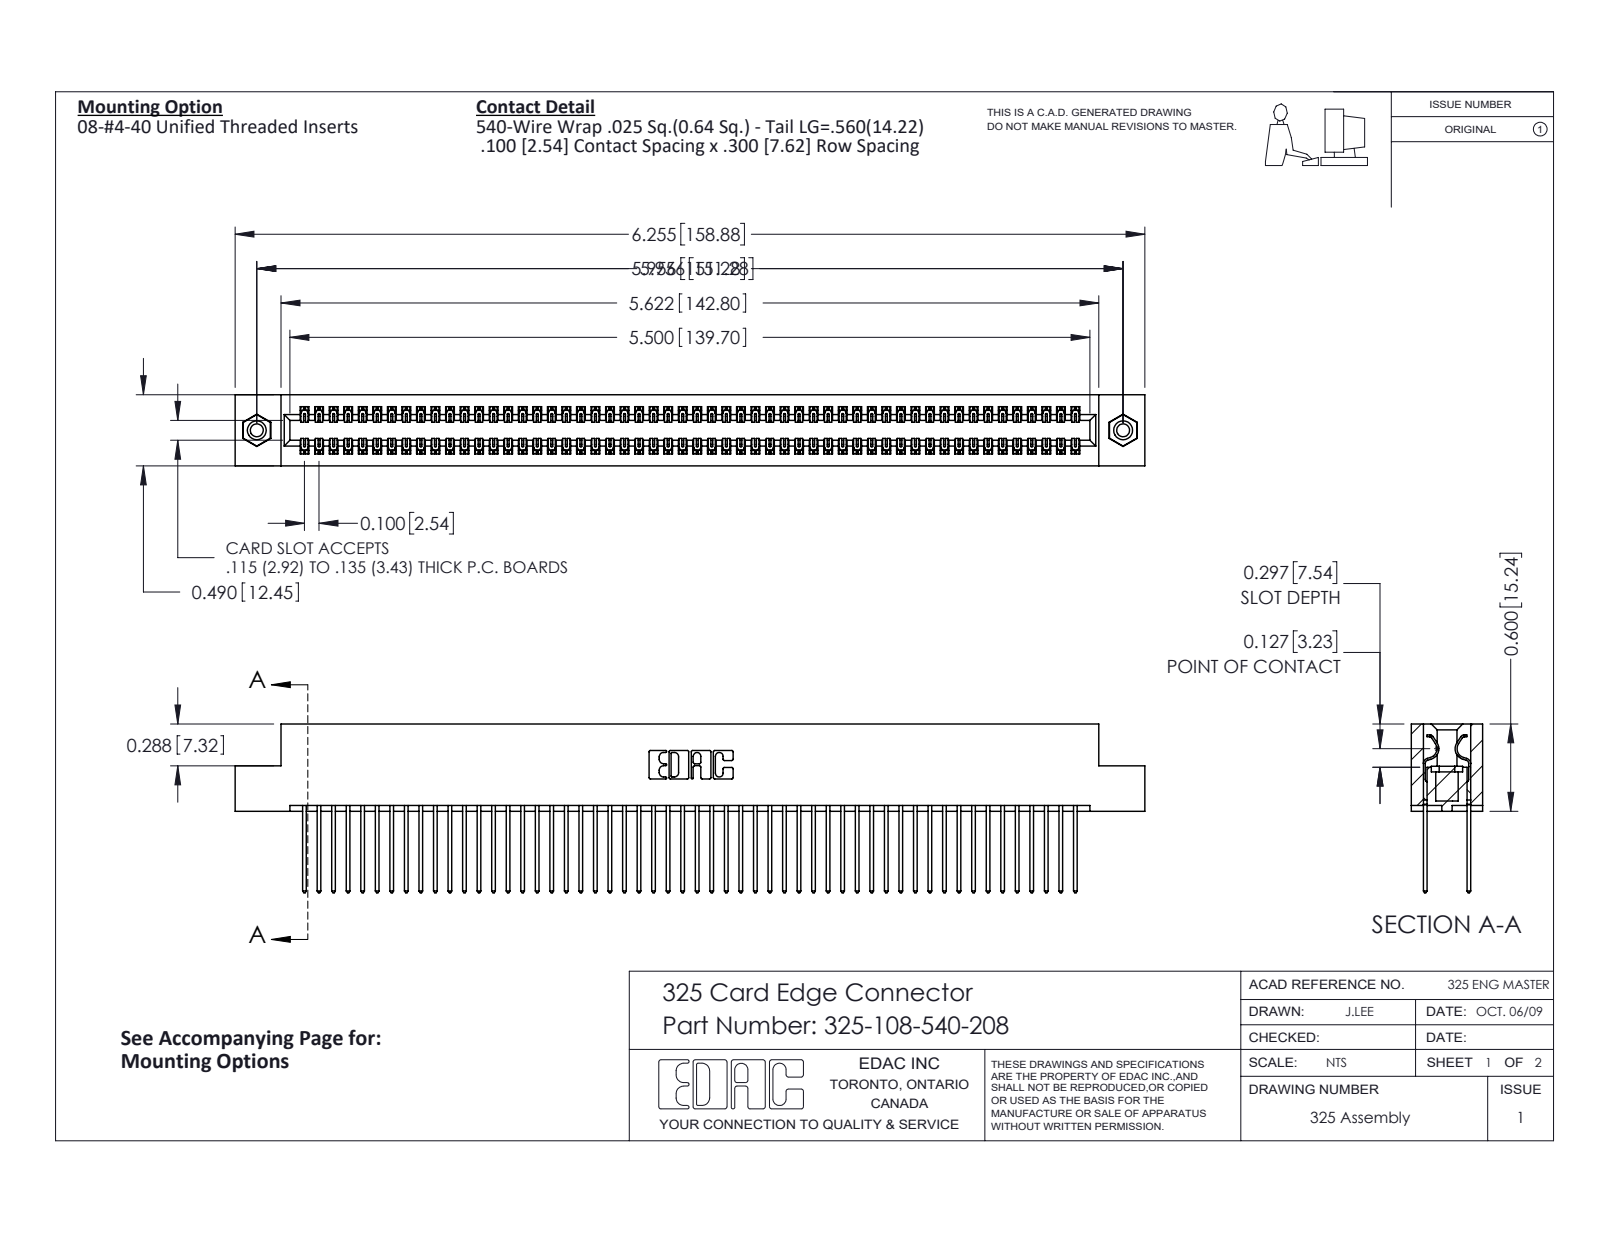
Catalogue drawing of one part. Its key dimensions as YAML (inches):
part_name: "325-108-540-208; 325 Part_TI; 345-250-001_345-250-003-102; 325-292-001_325-293-140"
step_written_by: "SolidWorks 2016 (CONFIG_CONTROL_DESIGN)"
units: inches
bodies: {solids: 111, faces: 5790, planar: 3990, cylindrical: 1784, other: 16}
overall_size: [6.255, 1.16, 0.49]
volume: 1.283
surface_area: 42.92
round_holes:
  - {diameter: 0.089, count: 2}
  - {diameter: 0.125, count: 2}
  - {diameter: 0.16, count: 2}
round_bosses_or_shafts:
  - {diameter: 0.155, count: 2}
partial_cylinders:
  - {radius: 0.006, count: 162}
  - {radius: 0.01, count: 108}
  - {radius: 0.01, count: 22}
  - {radius: 0.007, count: 6}
  - {radius: 0.031, count: 6}
  - {radius: 0.026, count: 3}
  - {radius: 0.014, count: 2}
  - {radius: 0.022, count: 2}
face_to_face_distances: [0.083, 0.407, 0.3, 0.107, 0.383, 0.025, 0.325, 0.49, 0.275, 0.56]
hole_center_spacings: [5.956]
